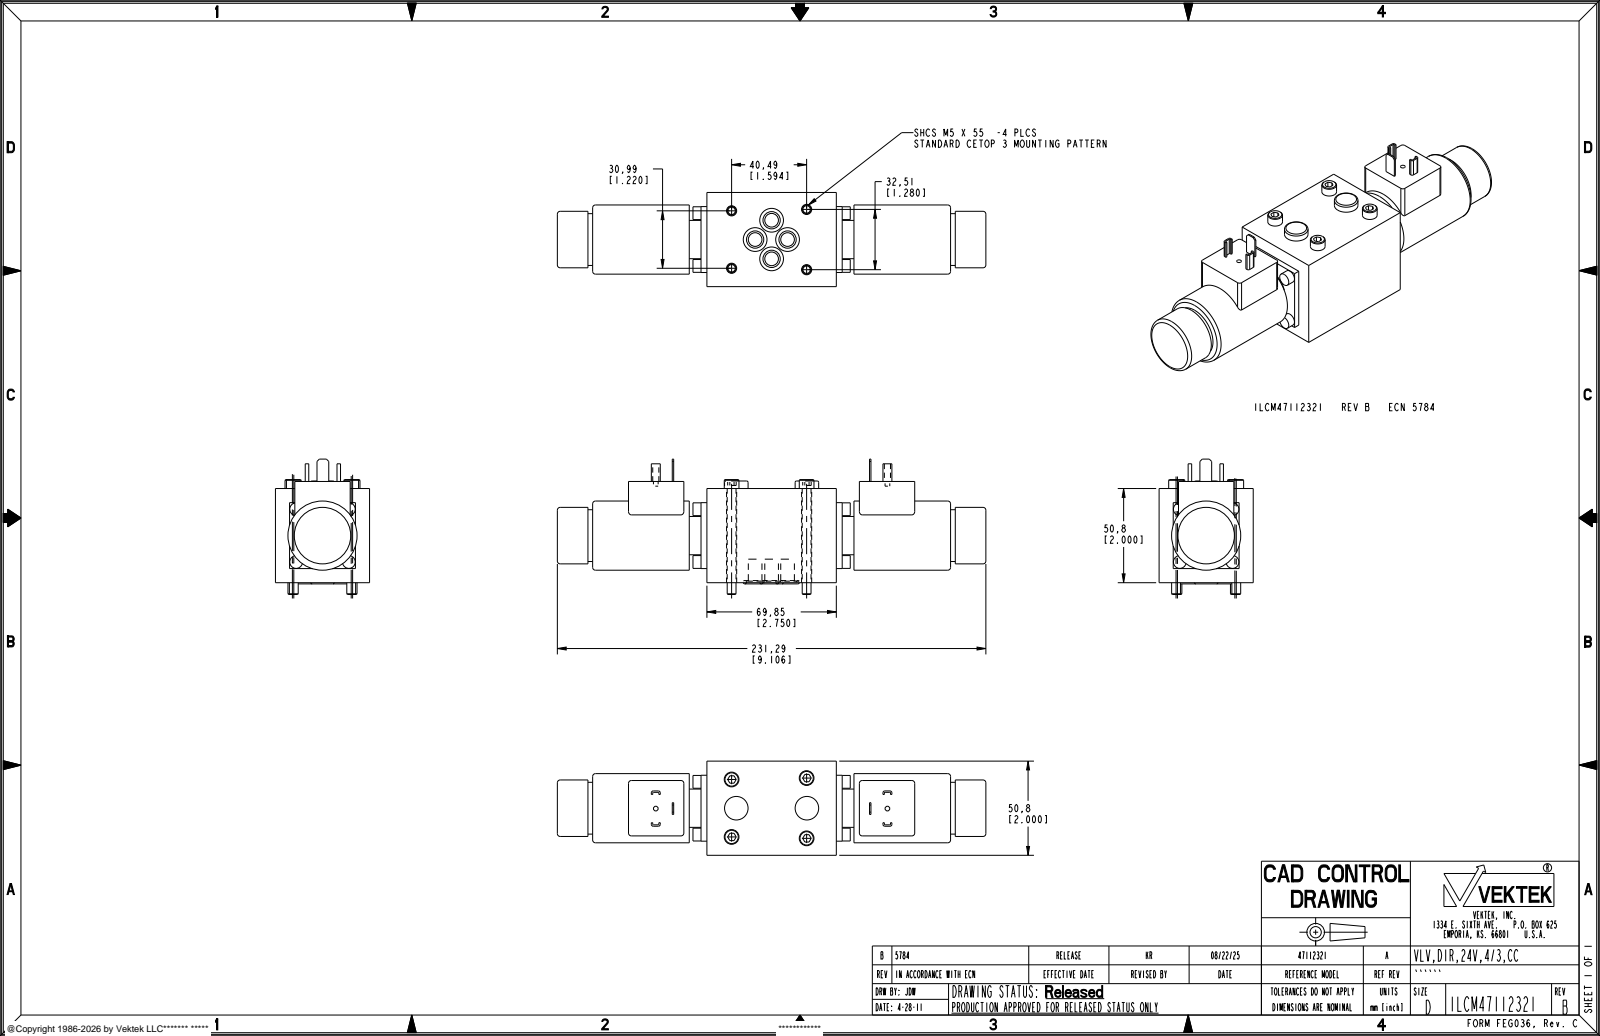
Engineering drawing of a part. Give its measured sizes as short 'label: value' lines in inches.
name: ILCM47112321
written by: CREO PARAMETRIC BY PTC INC, 2021164 (AUTOMOTIVE_DESIGN)
unit: in
bodies: 1 solid, 284 faces (144 planar, 104 cylindrical, 36 other)
size: 9.106 × 2.875 × 2
volume: 21.78 in³; area: 84.74 in²
holes: 4× ⌀0.215, 4× ⌀0.29, 4× ⌀0.49, 2× ⌀0.1
bosses: 4× ⌀0.313, 4× ⌀0.272, 4× ⌀0.187, 2× ⌀0.5, 1× ⌀1.469, 1× ⌀1.2, 1× ⌀1.1, 1× ⌀0.813
rounds: 8× R0.015, 8× R0.04, 8× R0.06
face distances: 2, 0.412, 1.588, 2.15, 0.15, 0.25, 0.125, 2.875, 0.375, 3.125
hole spacings: 0.532, 0.539, 0.757, 0.779, 0.789, 0.873, 1.268, 1.287
